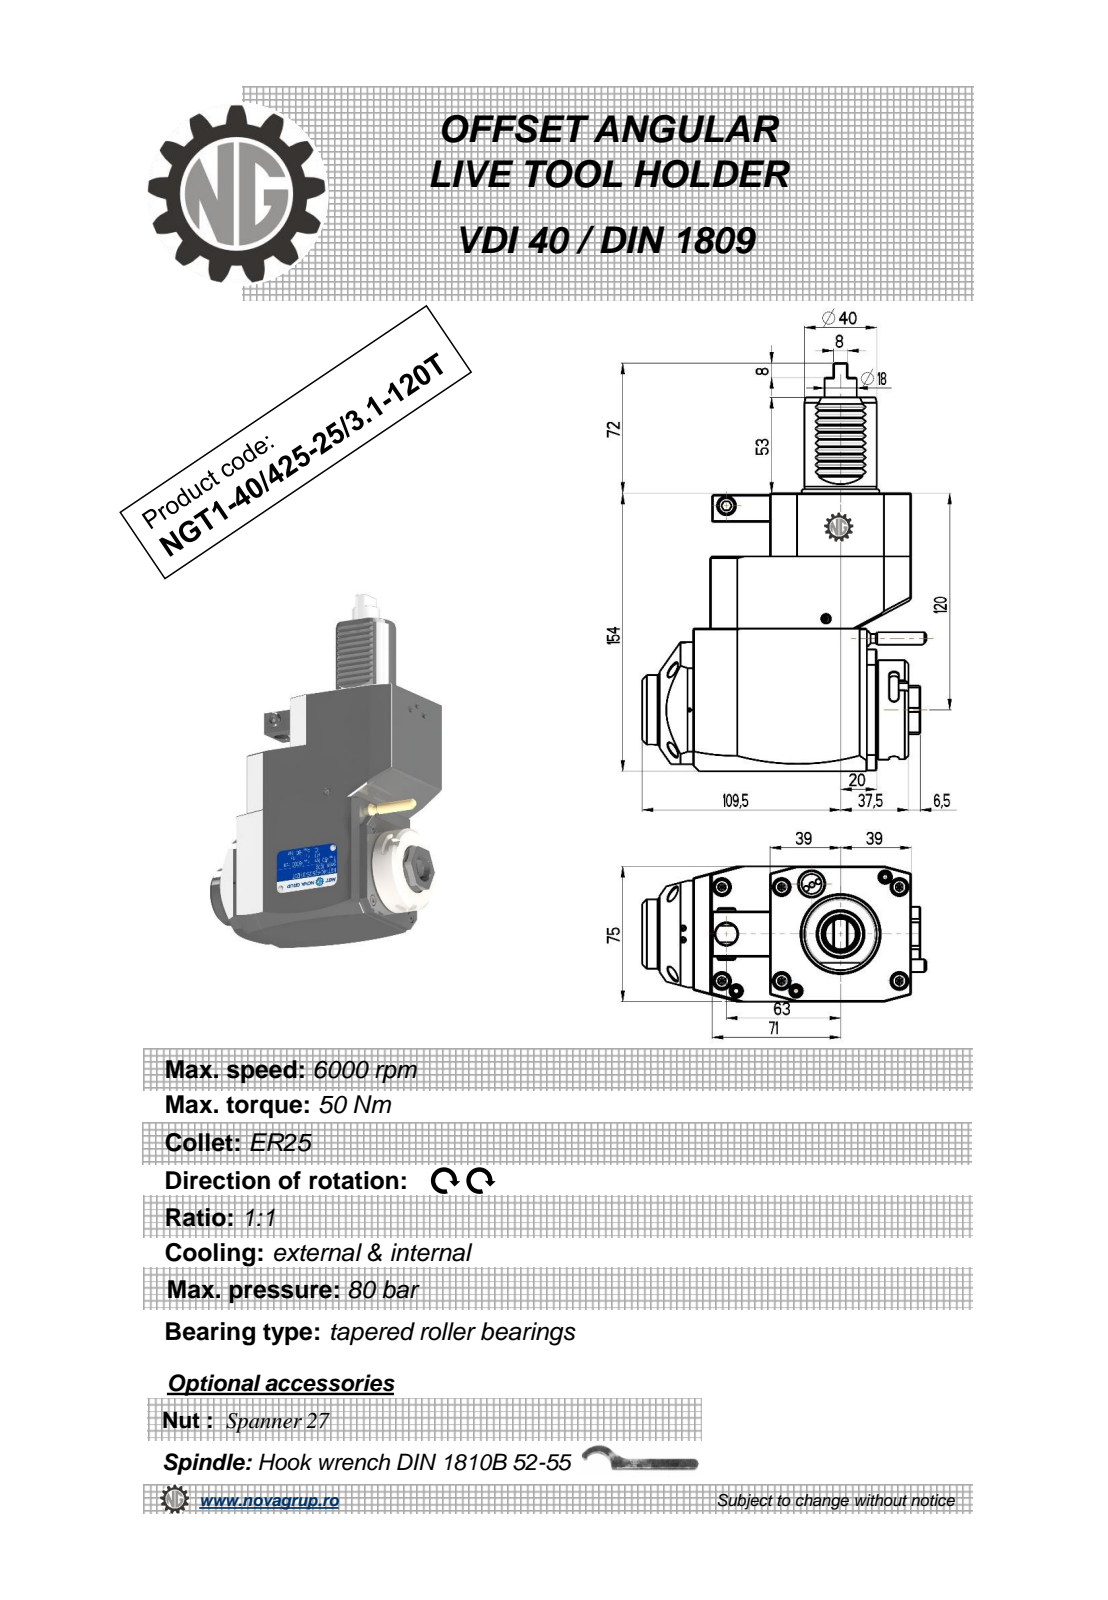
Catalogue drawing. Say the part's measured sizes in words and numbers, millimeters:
The part is named "NGT1_40_425_25_3_1_120T". Its 3-D file was written by "PRO/ENGINEER BY PARAMETRIC TECHNOLOGY CORPORATION, 2010280 (CONFIG_CONTROL_DESIGN)". It is 1 solid with 331 faces: 189 planar, 72 cylindrical and 70 other. Overall it measures 226 by 156.83 by 75 millimeters. Its volume is 1 270 000 cubic millimeters and its surface area 88 713 square millimeters. Round holes: 1 of diameter 2.5, 1 of diameter 3, 1 of diameter 9.5, 1 of diameter 12, 1 of diameter 18. Round bosses or shafts: 2 of diameter 8.96, 1 of diameter 55, 1 of diameter 48, 1 of diameter 40, 1 of diameter 38.5, 1 of diameter 17.8, 1 of diameter 10, 1 of diameter 7. Partial cylindrical surfaces (rounded edges, fillets, slot ends): 10 of radius 0.3, 6 of radius 2.5, 2 of radius 0.8, 2 of radius 180, 1 of radius 0.5, 1 of radius 4.25, 1 of radius 15, 1 of radius 24.5. The main face-to-face distances are 75, 154, 19, 119, 59, 111, 35, 92, 33, 17.5. The hole center spacings are 43.2, 75.07, 112.5.
